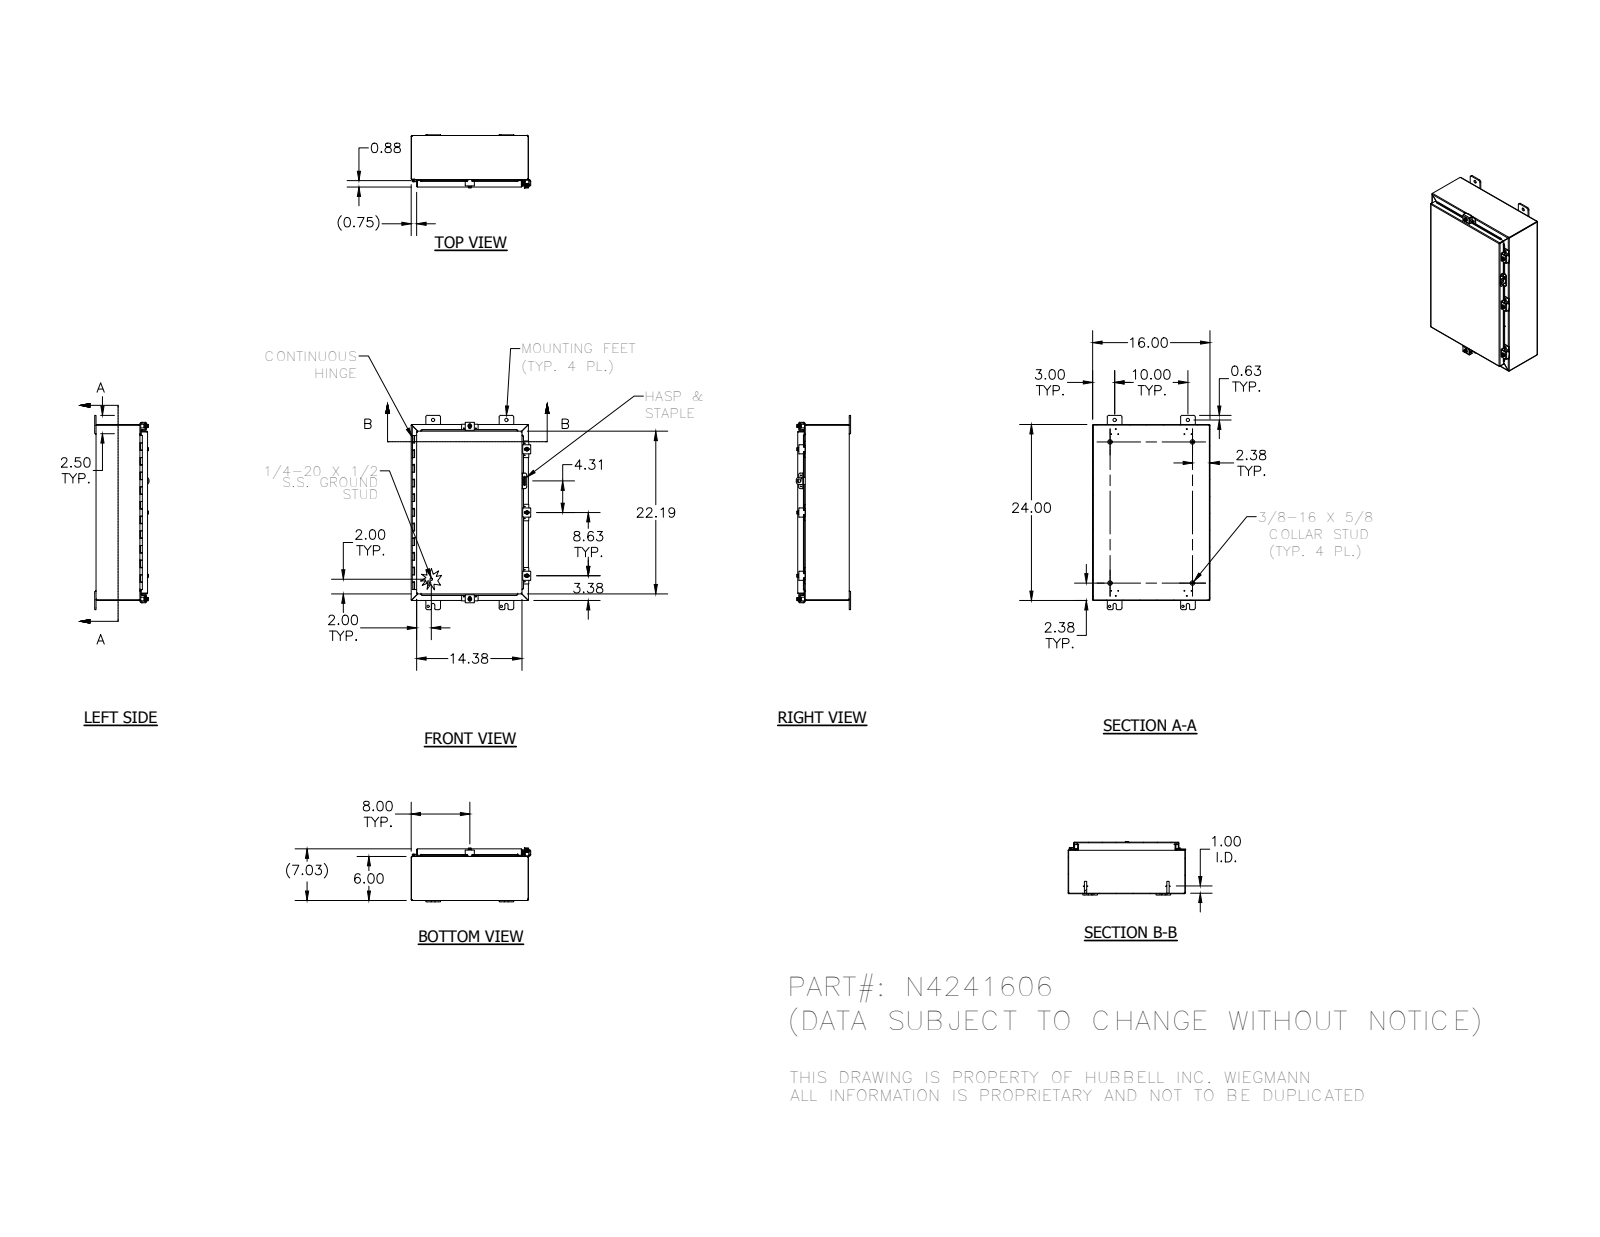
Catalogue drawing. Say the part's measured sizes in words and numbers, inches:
The part is named "328105P-1_1; 328105L_1; 328105T_1; N42416LID_1 (+8 more)". Its 3-D file was written by "SolidWorks 2014 (AUTOMOTIVE_DESIGN)". It is 42 solids with 1854 faces: 722 planar, 833 cylindrical and 299 other. Overall it measures 26.5 by 16.311 by 7.41 inches. Its volume is 121.3 cubic inches and its surface area 3 142 square inches. Round holes: 13 of diameter 0.11, 12 of diameter 0.12, 5 of diameter 0.211, 5 of diameter 0.281, 5 of diameter 0.3, 4 of diameter 0.313, 4 of diameter 0.438, 1 of diameter 0.125, 1 of diameter 0.156, 1 of diameter 0.5. Round bosses or shafts: 7 of diameter 0.25, 5 of diameter 0.52, 5 of diameter 0.5, 5 of diameter 0.35, 4 of diameter 0.625, 4 of diameter 0.33, 2 of diameter 0.115, 1 of diameter 0.337. Partial cylindrical surfaces (rounded edges, fillets, slot ends): 61 of radius 0.03, 37 of radius 0.062, 35 of radius 0.125, 31 of radius 0.25, 23 of radius 0.031, 23 of radius 0.105, 10 of radius 0.141, 8 of radius 0.063. The main face-to-face distances are 0.074, 6.959, 6.885, 7.033, 15.926, 5.926, 1.033, 23.926, 15.852, 16. The hole center spacings are 10, 0.876, 0.759, 0.839, 0.94, 0.969, 1.593, 1.995.
